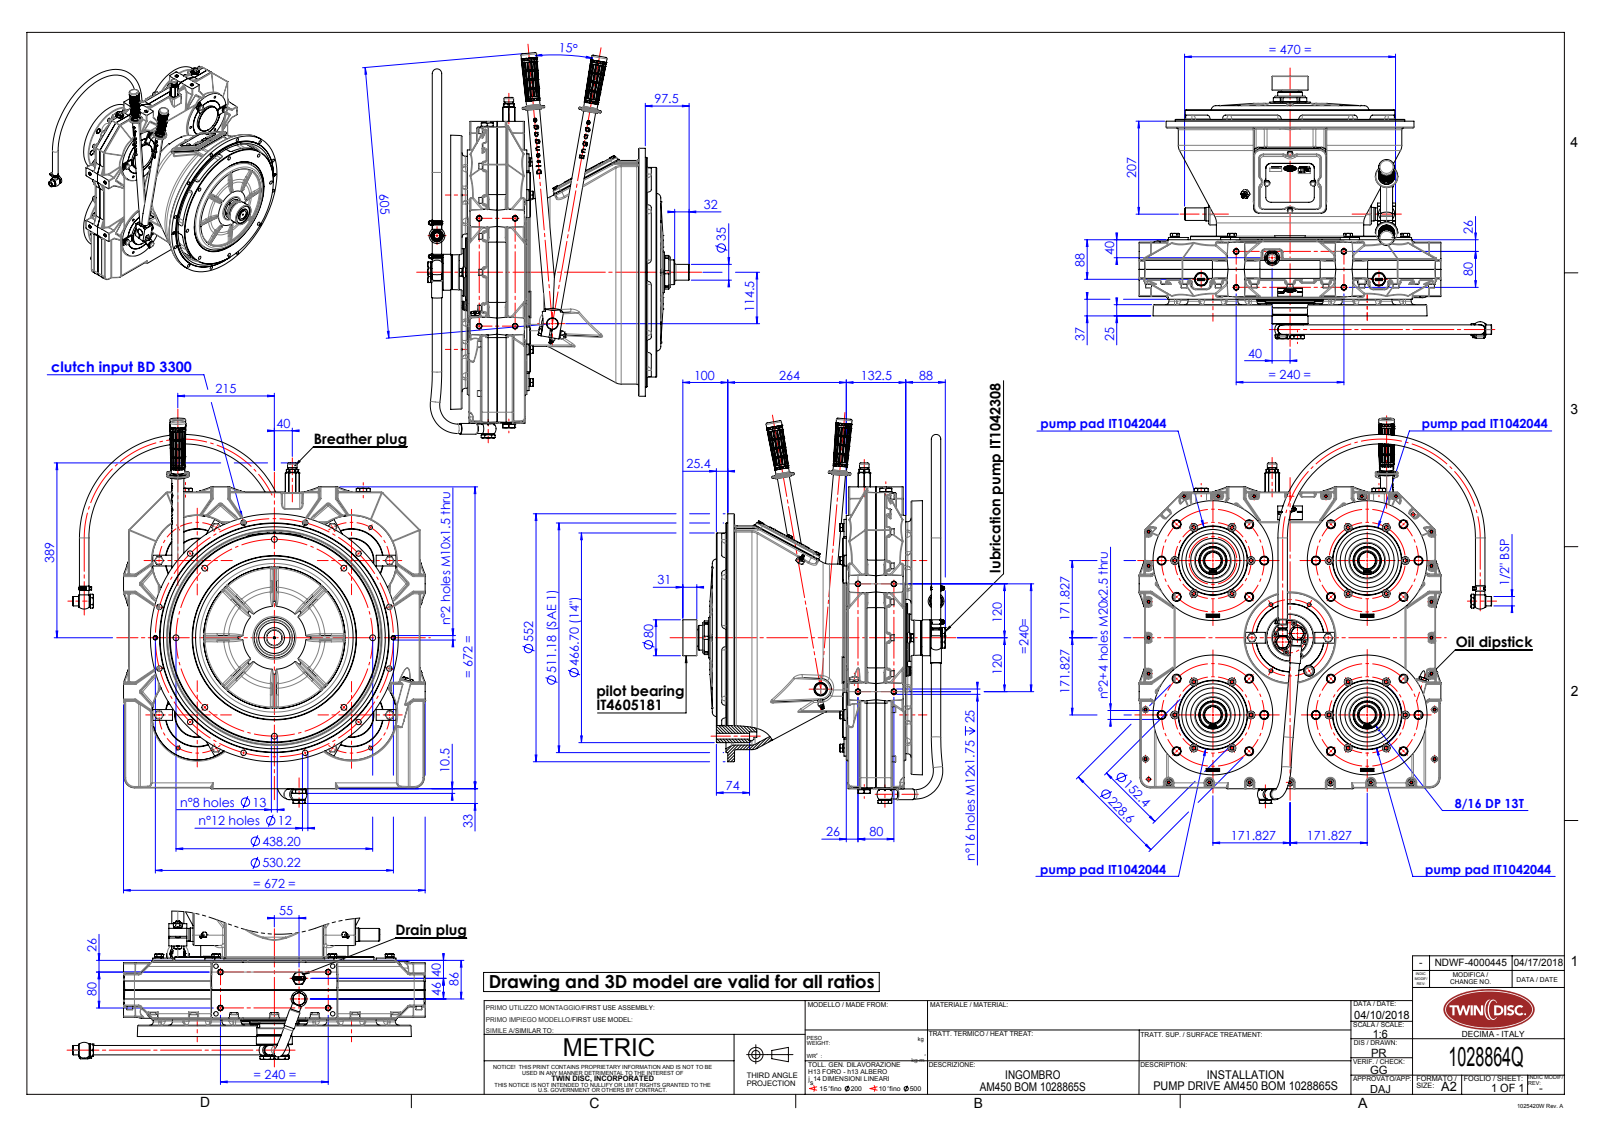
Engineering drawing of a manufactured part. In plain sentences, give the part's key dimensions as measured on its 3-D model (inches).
The part is named "IT2021216_rev03-installation; IT4588040_rev00-installation; IT1042044_rev00-installation; IT1042308-installation (+8 more)". Its 3-D file was written by "SolidWorks 2015 (AUTOMOTIVE_DESIGN)". It is 98 solids with 12867 faces: 6385 planar, 2813 cylindrical and 3669 other. Overall it measures 33.778 by 30.915 by 23.012 inches. Its volume is 495.8 cubic inches and its surface area 10 590 square inches. Round holes: 70 of diameter 0.335, 33 of diameter 0.433, 26 of diameter 0.402, 26 of diameter 0.669, 24 of diameter 0.689, 22 of diameter 0.512, 21 of diameter 0.472, 12 of diameter 0.394, 11 of diameter 0.197, 11 of diameter 0.276, 10 of diameter 0.315, 10 of diameter 0.827. Round bosses or shafts: 37 of diameter 0.394, 28 of diameter 0.512, 28 of diameter 0.315, 25 of diameter 0.787, 24 of diameter 0.63, 13 of diameter 0.638, 12 of diameter 0.713, 11 of diameter 0.236. Partial cylindrical surfaces (rounded edges, fillets, slot ends): 324 of radius 0.098, 108 of radius 0.079, 83 of radius 0.315, 58 of radius 0.014, 58 of radius 1.163, 50 of radius 0.118, 36 of radius 0.197, 31 of radius 0.059. The main face-to-face distances are 5.059, 0.157, 2.461, 2.598, 1.614, 4.075, 6.673, 0.984, 5.531, 0.472. The hole center spacings are 3.346, 4.724, 7.023, 9.567, 10.012, 2.26, 2.953, 4.208.
